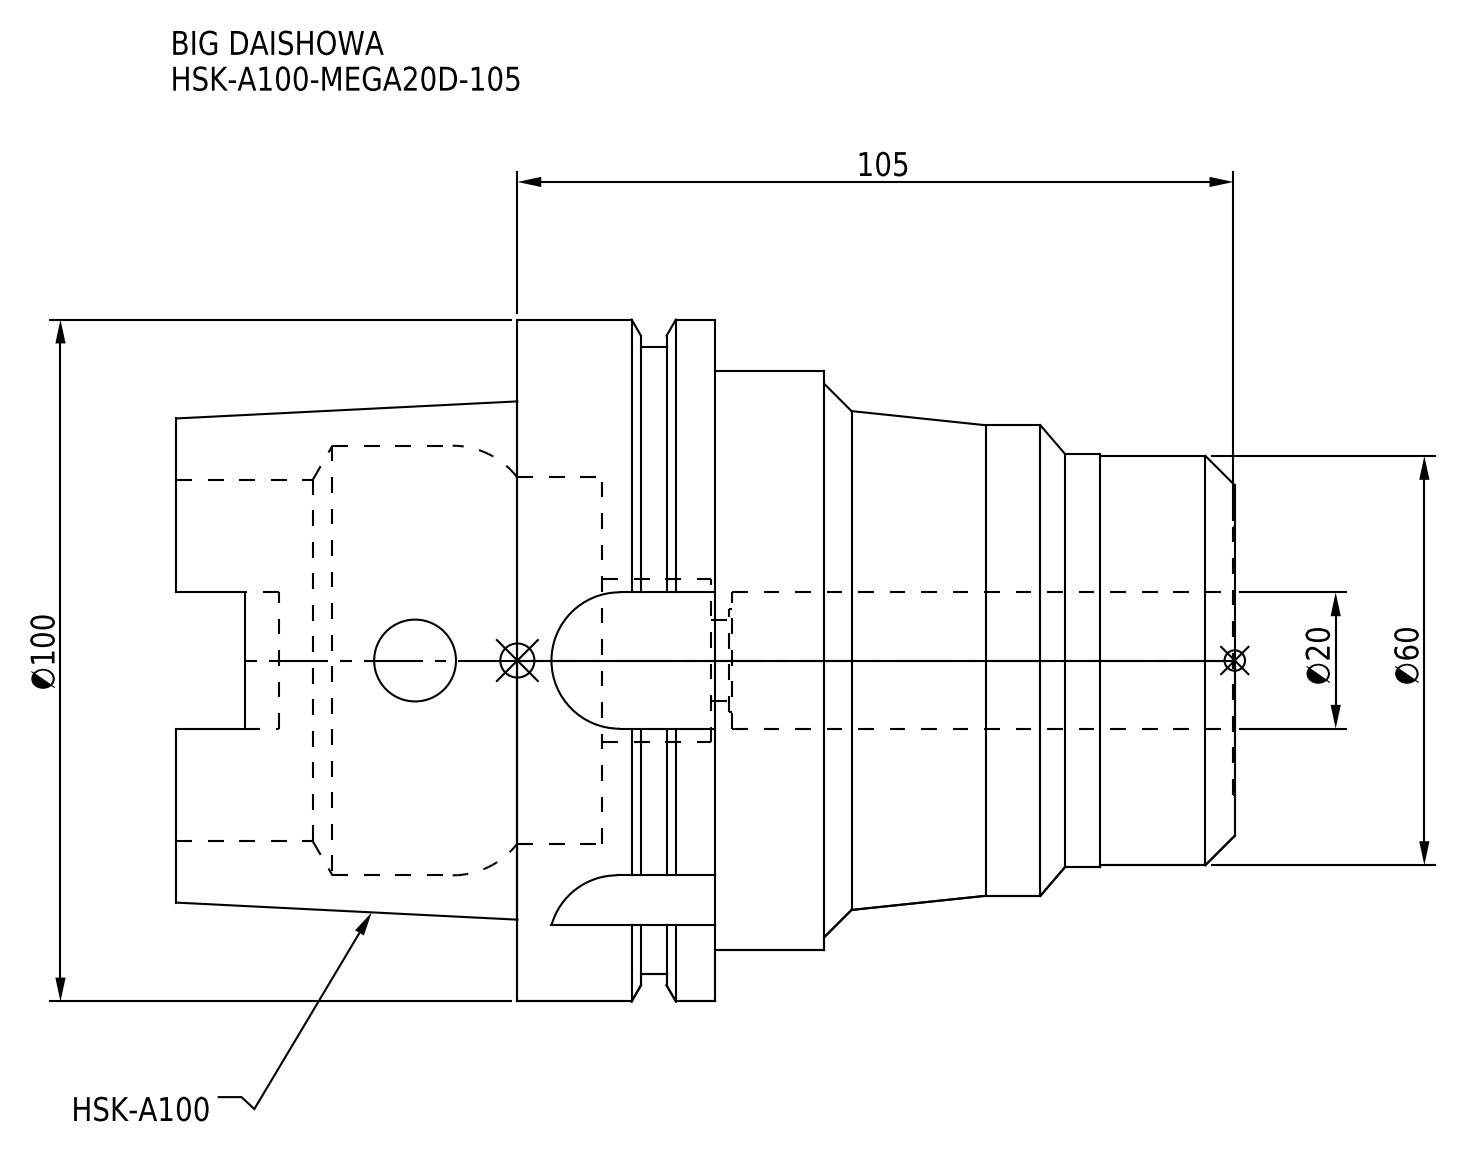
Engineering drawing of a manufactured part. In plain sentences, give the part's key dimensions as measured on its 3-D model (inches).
The part is named "HSK-A100-MEGA20D-105". Its 3-D file was written by "CREO PARAMETRIC BY PTC INC, 2016380 (AUTOMOTIVE_DESIGN)". It is 1 solid with 105 faces: 37 planar, 46 cylindrical and 22 other. Overall it measures 6.11 by 3.937 by 3.937 inches. Its volume is 32.24 cubic inches and its surface area 107.5 square inches. Round holes: 2 of diameter 0.472, 1 of diameter 0.591, 1 of diameter 0.787, 1 of diameter 0.945, 1 of diameter 1.547, 1 of diameter 2.087, 1 of diameter 2.118, 1 of diameter 2.48. Round bosses or shafts: 1 of diameter 3.937, 1 of diameter 3.622, 1 of diameter 3.346, 1 of diameter 2.717, 1 of diameter 2.39, 1 of diameter 2.362. Partial cylindrical surfaces (rounded edges, fillets, slot ends): 4 of radius 0.192, 4 of radius 0.394. The main face-to-face distances are 0.652, 1.142, 0.49, 3.11, 2.459, 1.969, 2.992, 3.644, 4.134, 6.102.
